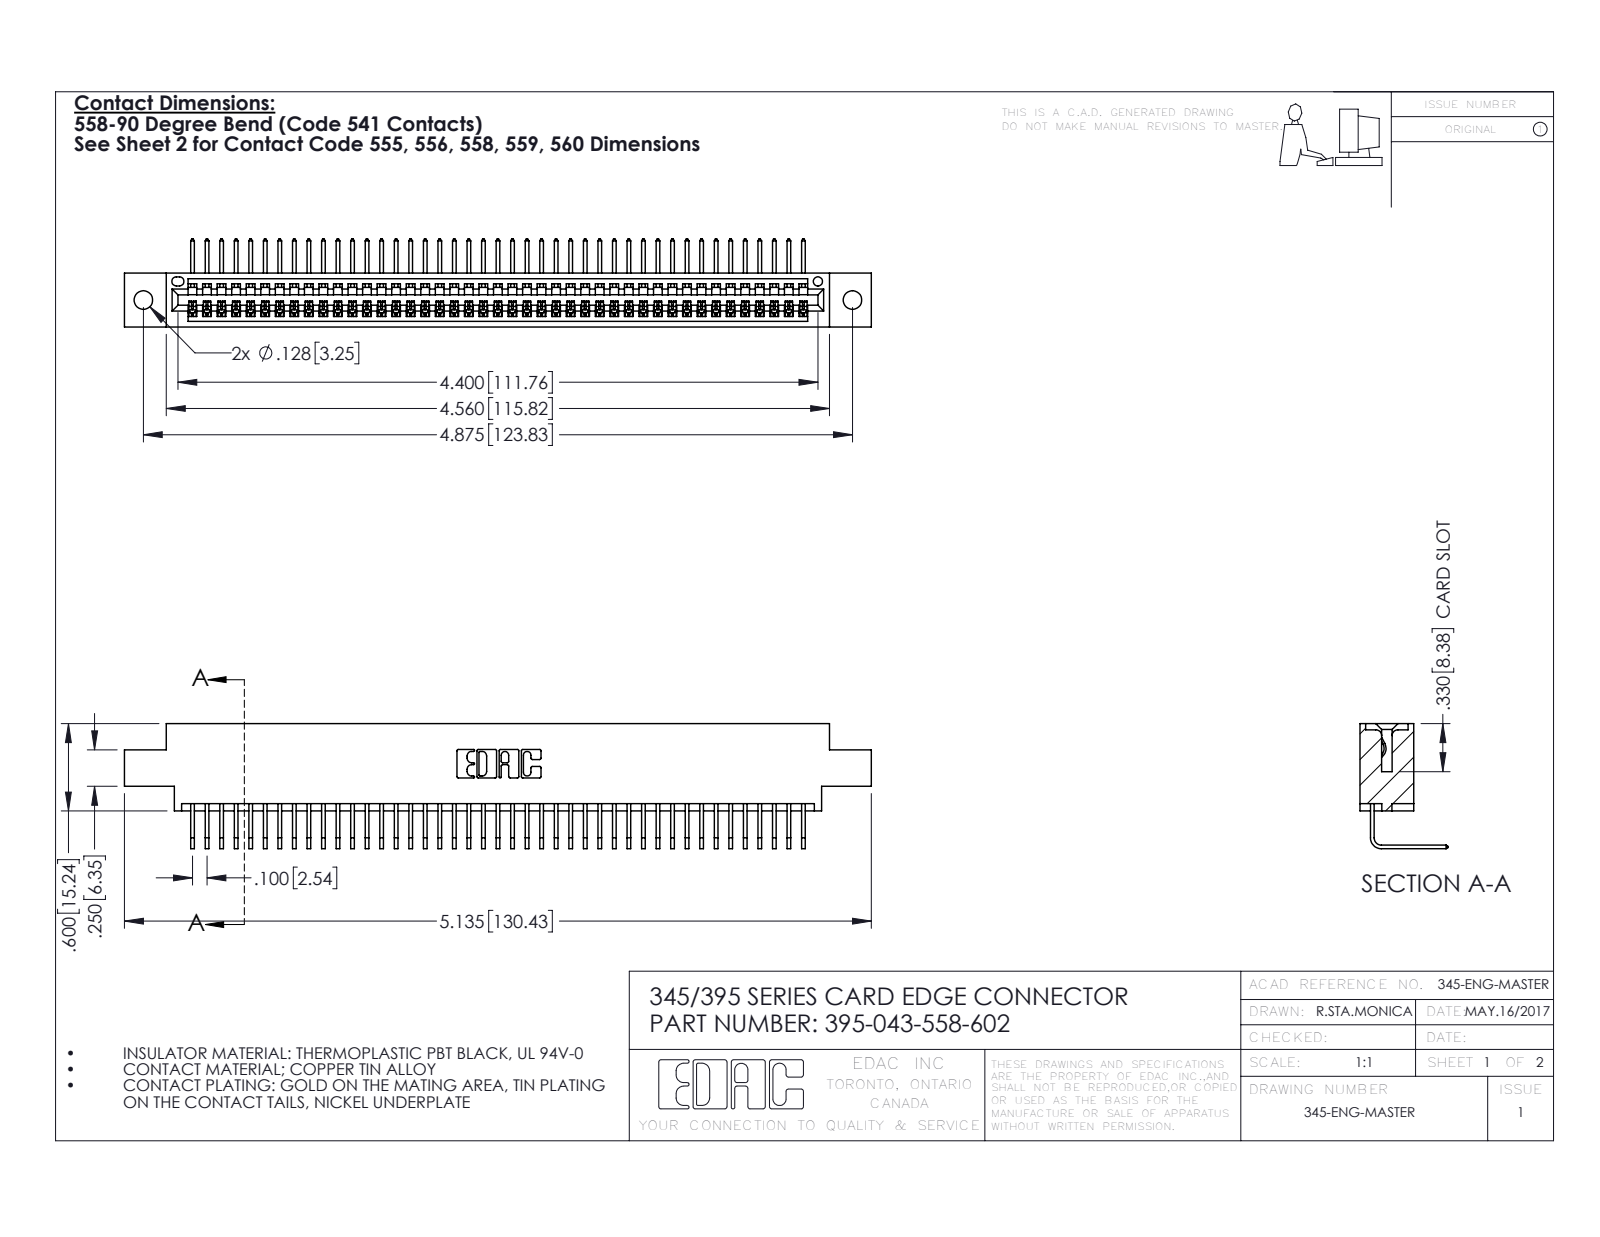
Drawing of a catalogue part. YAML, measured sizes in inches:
part_name: "345-292-001_558 Tail - 2; 345 Part_0.170 Offset - 0.128 Dia; 395-043-558-602"
step_written_by: "SolidWorks 2016 (CONFIG_CONTROL_DESIGN)"
units: inches
bodies: {solids: 44, faces: 2710, planar: 1890, cylindrical: 820, other: 0}
overall_size: [5.135, 0.859, 0.605]
volume: 0.756
surface_area: 26.62
round_holes:
  - {diameter: 0.128, count: 2}
  - {diameter: 0.064, count: 1}
partial_cylinders:
  - {radius: 0.006, count: 86}
  - {radius: 0.01, count: 22}
  - {radius: 0.007, count: 6}
  - {radius: 0.031, count: 6}
  - {radius: 0.026, count: 3}
  - {radius: 0.031, count: 2}
  - {radius: 0.04, count: 2}
  - {radius: 0.014, count: 1}
face_to_face_distances: [0.072, 0.298, 0.37, 0.2, 0.098, 0.272, 0.025, 0.225, 0.175, 0.149]
hole_center_spacings: [0.27, 4.639, 4.875]
